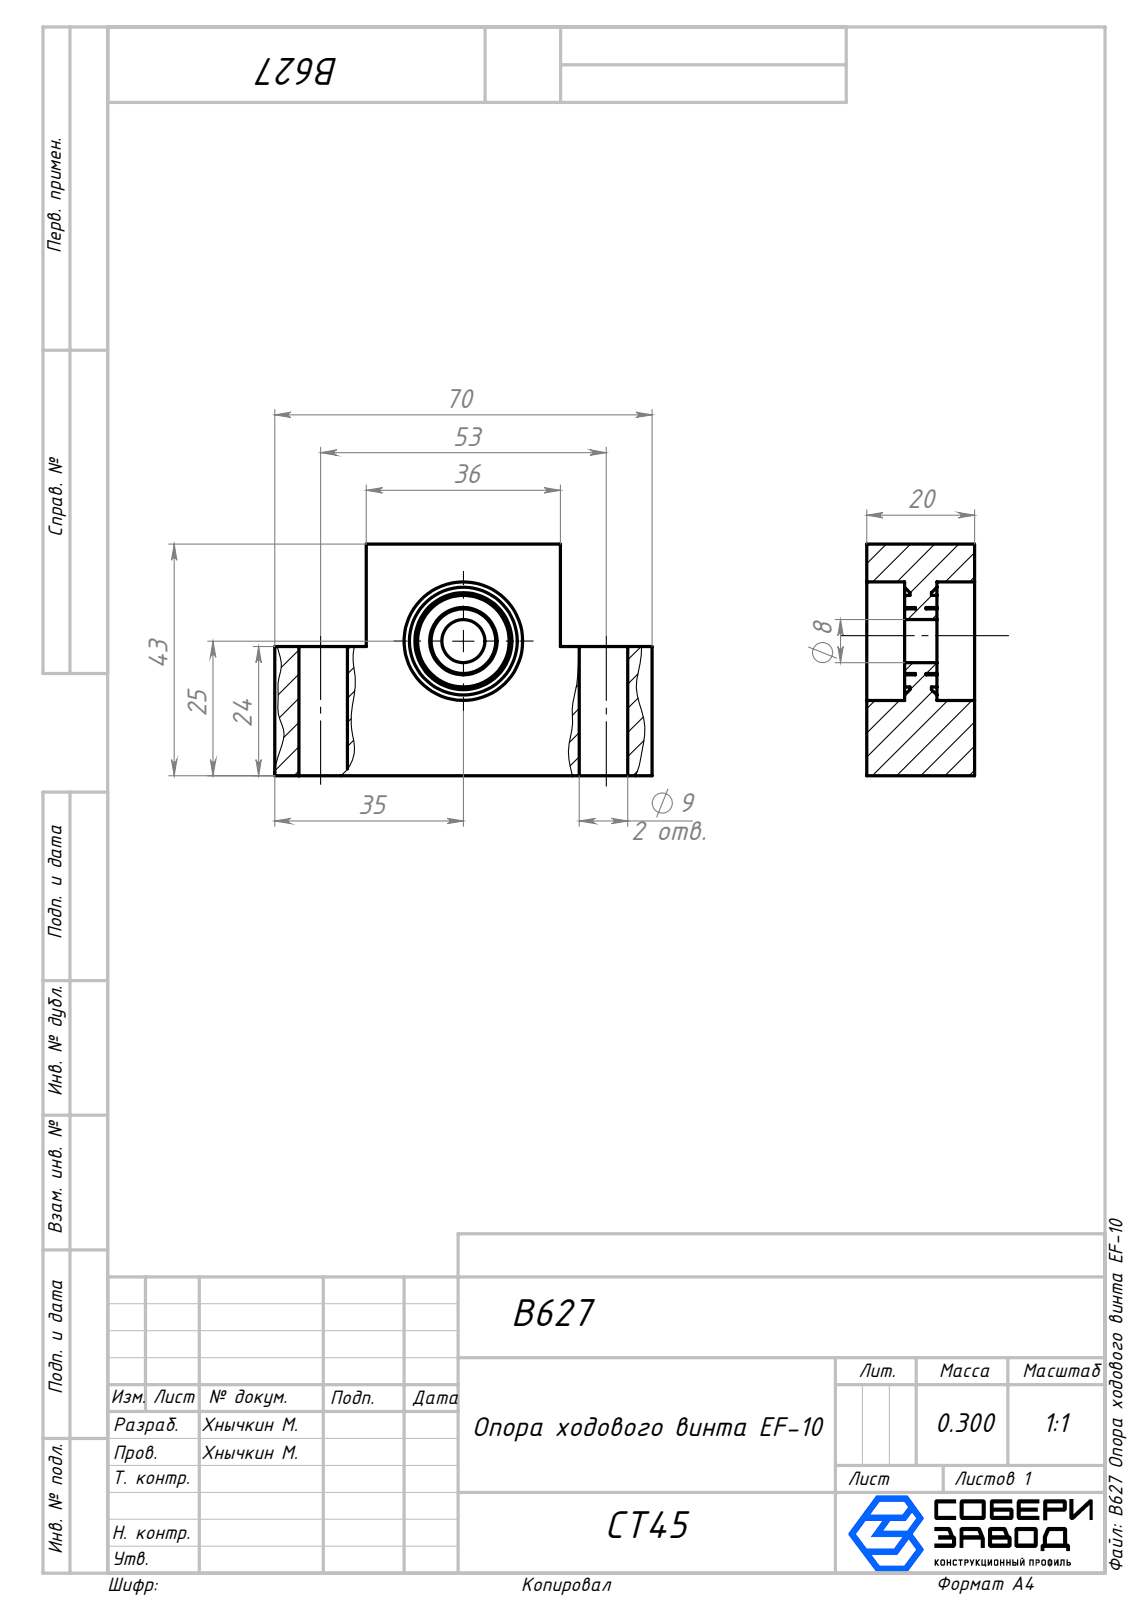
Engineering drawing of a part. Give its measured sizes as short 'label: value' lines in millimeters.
name: B627 Опора ходового винта EF-10
written by: SolidWorks 2026 (AUTOMOTIVE_DESIGN)
unit: mm
bodies: 1 solid, 46 faces (20 planar, 22 cylindrical, 4 other)
size: 70 × 43 × 20
volume: 38 451 mm³; area: 11 833 mm²
holes: 2× ⌀9, 1× ⌀8, 1× ⌀12.5, 1× ⌀22
bosses: 1× ⌀17, 1× ⌀12
face distances: 20, 17, 53, 43, 24, 19, 70, 7, 13, 36
hole spacings: 52
